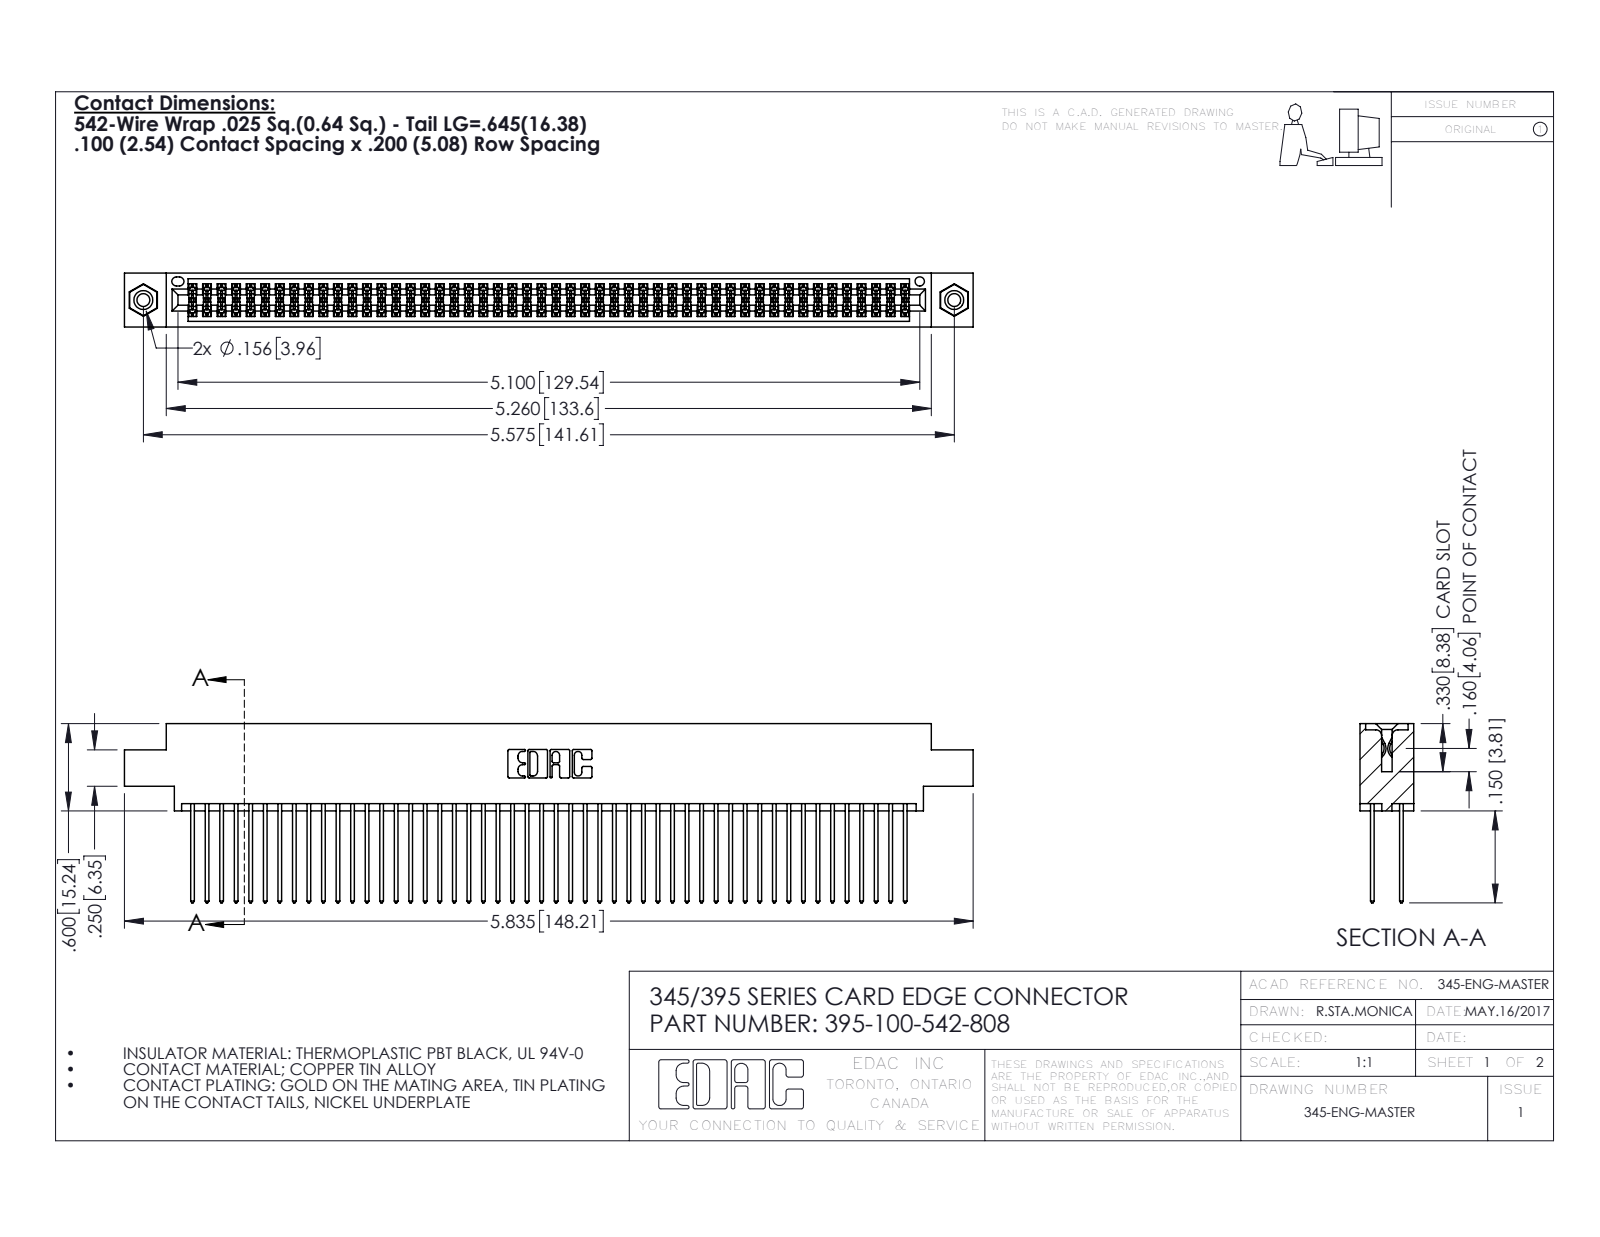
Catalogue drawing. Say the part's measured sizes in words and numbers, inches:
The part is named "345 Part_0.170 Offset - 0.156 Dia-TI; 395-100-542-808; 345-292-001_345-293-142; 345-250-001_345-250-003-102". Its 3-D file was written by "SolidWorks 2016 (CONFIG_CONTROL_DESIGN)". It is 103 solids with 5190 faces: 3416 planar, 1758 cylindrical and 16 other. Overall it measures 5.835 by 1.232 by 0.37 inches. Its volume is 0.904 cubic inches and its surface area 37.81 square inches. Round holes: 2 of diameter 0.089, 2 of diameter 0.125, 2 of diameter 0.156, 1 of diameter 0.064. Round bosses or shafts: 2 of diameter 0.155. Partial cylindrical surfaces (rounded edges, fillets, slot ends): 150 of radius 0.006, 100 of radius 0.01, 22 of radius 0.01, 6 of radius 0.007, 6 of radius 0.031, 3 of radius 0.026, 2 of radius 0.014, 2 of radius 0.019. The main face-to-face distances are 0.072, 0.298, 0.2, 0.098, 0.272, 0.025, 0.37, 0.225, 0.175, 0.149. The hole center spacings are 0.27, 5.339, 5.575.
